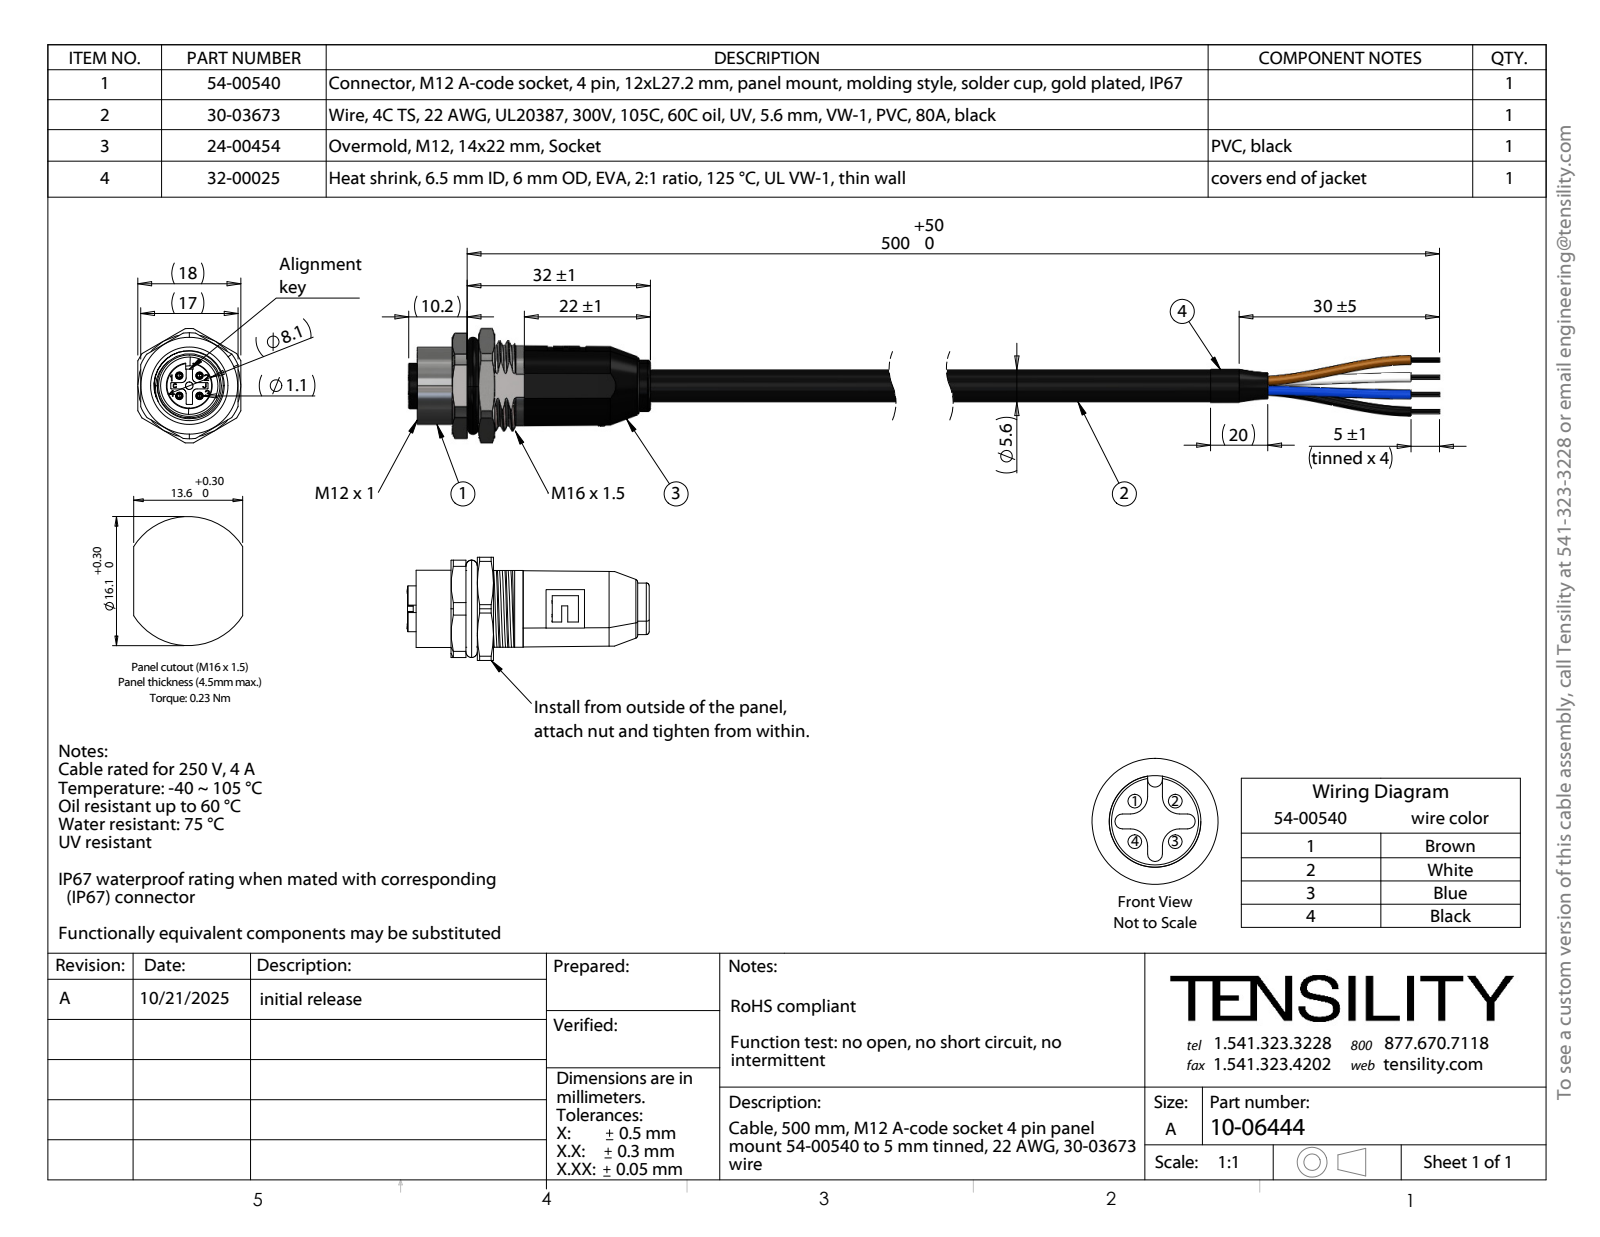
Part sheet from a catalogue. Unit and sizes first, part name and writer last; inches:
Units: inches
Overall size (bounding box): 8.946 × 0.787 × 0.709
Round holes (diameter × count): ⌀0.063 ×8, ⌀0.051 ×5, ⌀0.047 ×4, ⌀0.153 ×1, ⌀0.169 ×1, ⌀0.256 ×1, ⌀0.295 ×1, ⌀0.346 ×1, ⌀0.358 ×1, ⌀0.378 ×1, ⌀0.441 ×1, ⌀0.48 ×1
Round bosses / shafts (diameter × count): ⌀0.067 ×4, ⌀0.061 ×4, ⌀0.06 ×4, ⌀0.549 ×1, ⌀0.531 ×1, ⌀0.492 ×1, ⌀0.433 ×1, ⌀0.421 ×1
Partial cylindrical surfaces — rounded edges, fillets, slot ends (radius × count): R0.004 ×6, R0.031 ×4, R0.02 ×3, R0.277 ×1, R0.311 ×1, R0.364 ×1, R0.394 ×1
Main face-to-face distances: 0.02, 0.394, 0.079, 0.374, 0.453, 0.709, 0.295, 0.102, 0.059, 0.201
Hole centre spacings: 0.019, 0.015, 0.064, 0.012, 0.013, 0.07, 0.013, 0.057
Volume: 0.607 in³ · Surface area: 53.82 in²
Bodies: 155 solids, 1614 faces (715 planar, 659 cylindrical, 240 other)
Part name (STEP PRODUCT): 54-00540; 32-00025_10 mm; 30-03673_spec; 24-00454 (+2 more)
STEP written by: SolidWorks 2025 (CONFIG_CONTROL_DESIGN)
